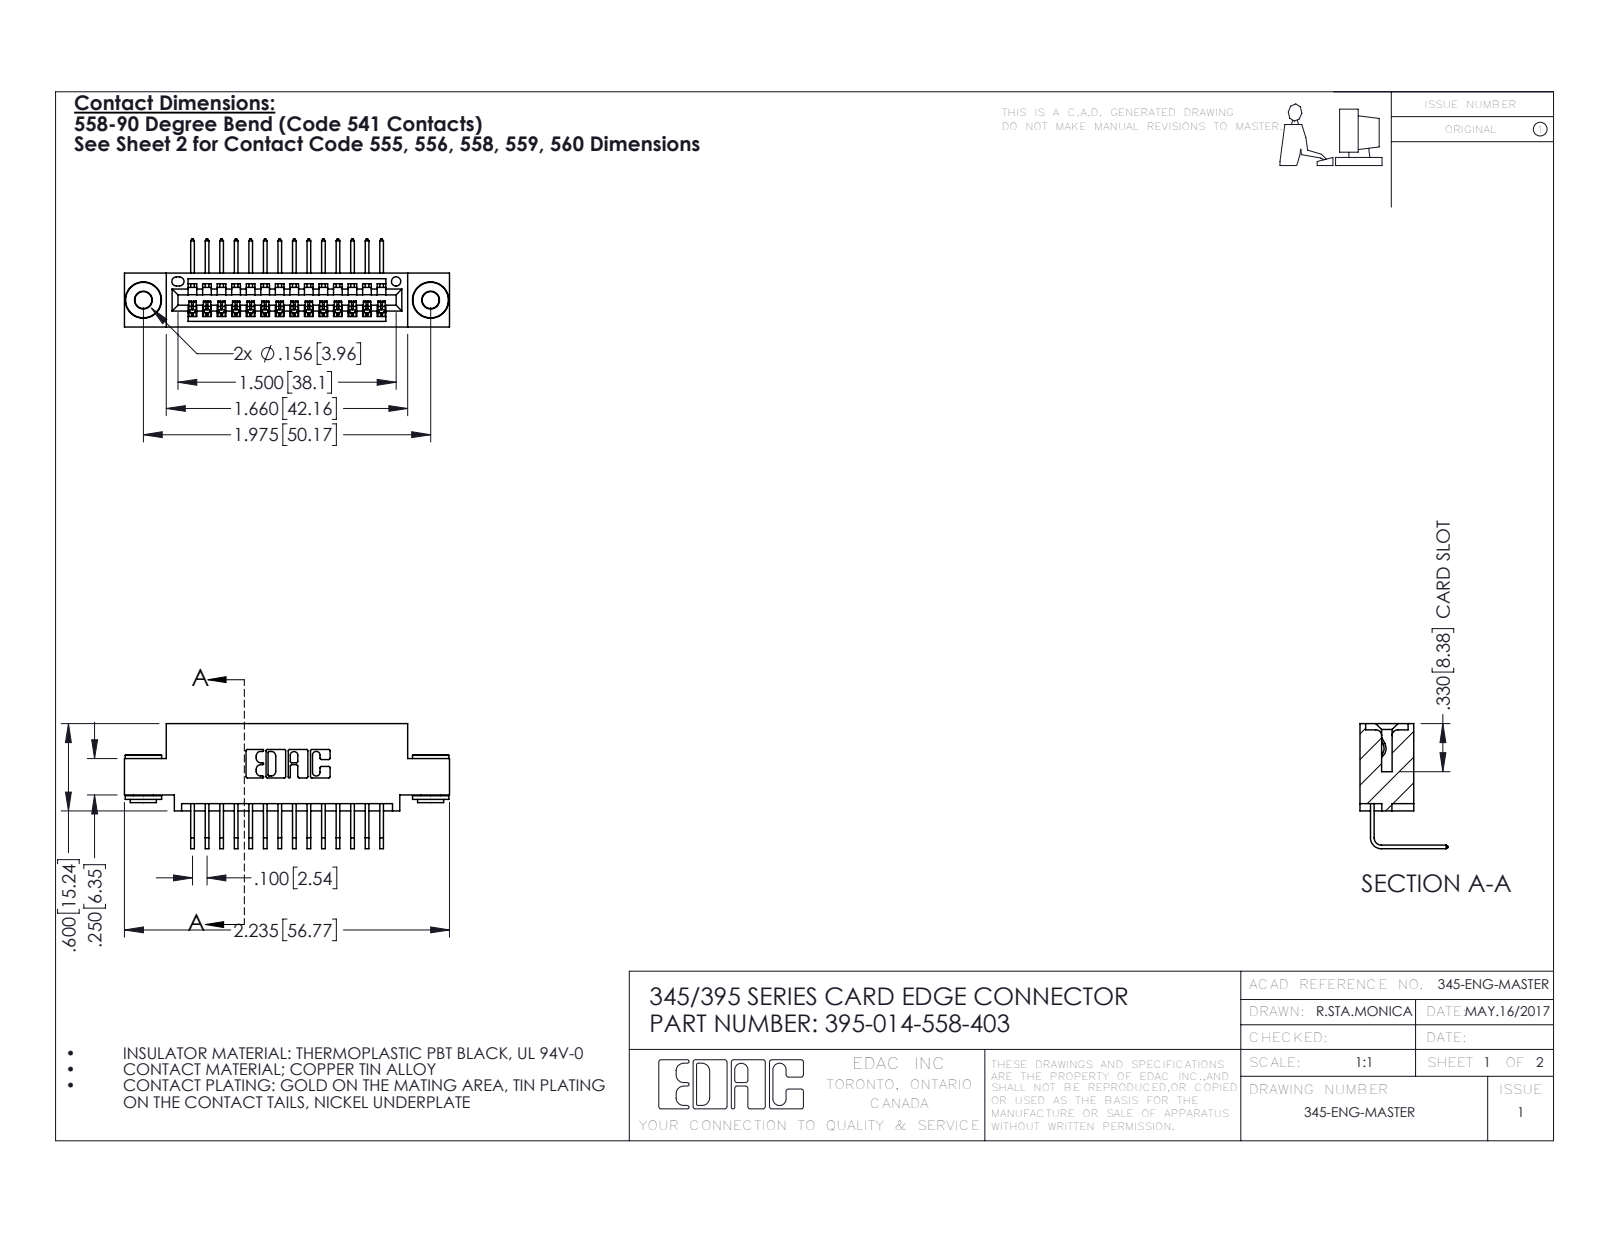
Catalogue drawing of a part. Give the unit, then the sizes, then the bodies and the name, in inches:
Units: inches
Overall size (bounding box): 2.235 × 0.859 × 0.605
Round holes (diameter × count): ⌀0.116 ×2, ⌀0.156 ×2, ⌀0.064 ×1
Round bosses / shafts (diameter × count): ⌀0.25 ×2, ⌀0.18 ×2, ⌀0.136 ×2
Partial cylindrical surfaces — rounded edges, fillets, slot ends (radius × count): R0.006 ×28, R0.01 ×22, R0.007 ×6, R0.031 ×6, R0.026 ×3, R0.031 ×2, R0.04 ×2, R0.014 ×1
Main face-to-face distances: 0.072, 0.298, 0.2, 0.37, 0.025, 0.098, 0.272, 0.225, 0.1, 0.3
Hole centre spacings: 0.27, 1.742, 1.975
Volume: 0.315 in³ · Surface area: 10.91 in²
Bodies: 17 solids, 1008 faces (682 planar, 318 cylindrical, 8 other)
Part name (STEP PRODUCT): 345 Part_0.110 Offset - 0.156 Dia-TH; 395-014-558-403; 345-292-001_558 Tail - 2; 345-250-002_345-250-002-102
STEP written by: SolidWorks 2016 (CONFIG_CONTROL_DESIGN)
